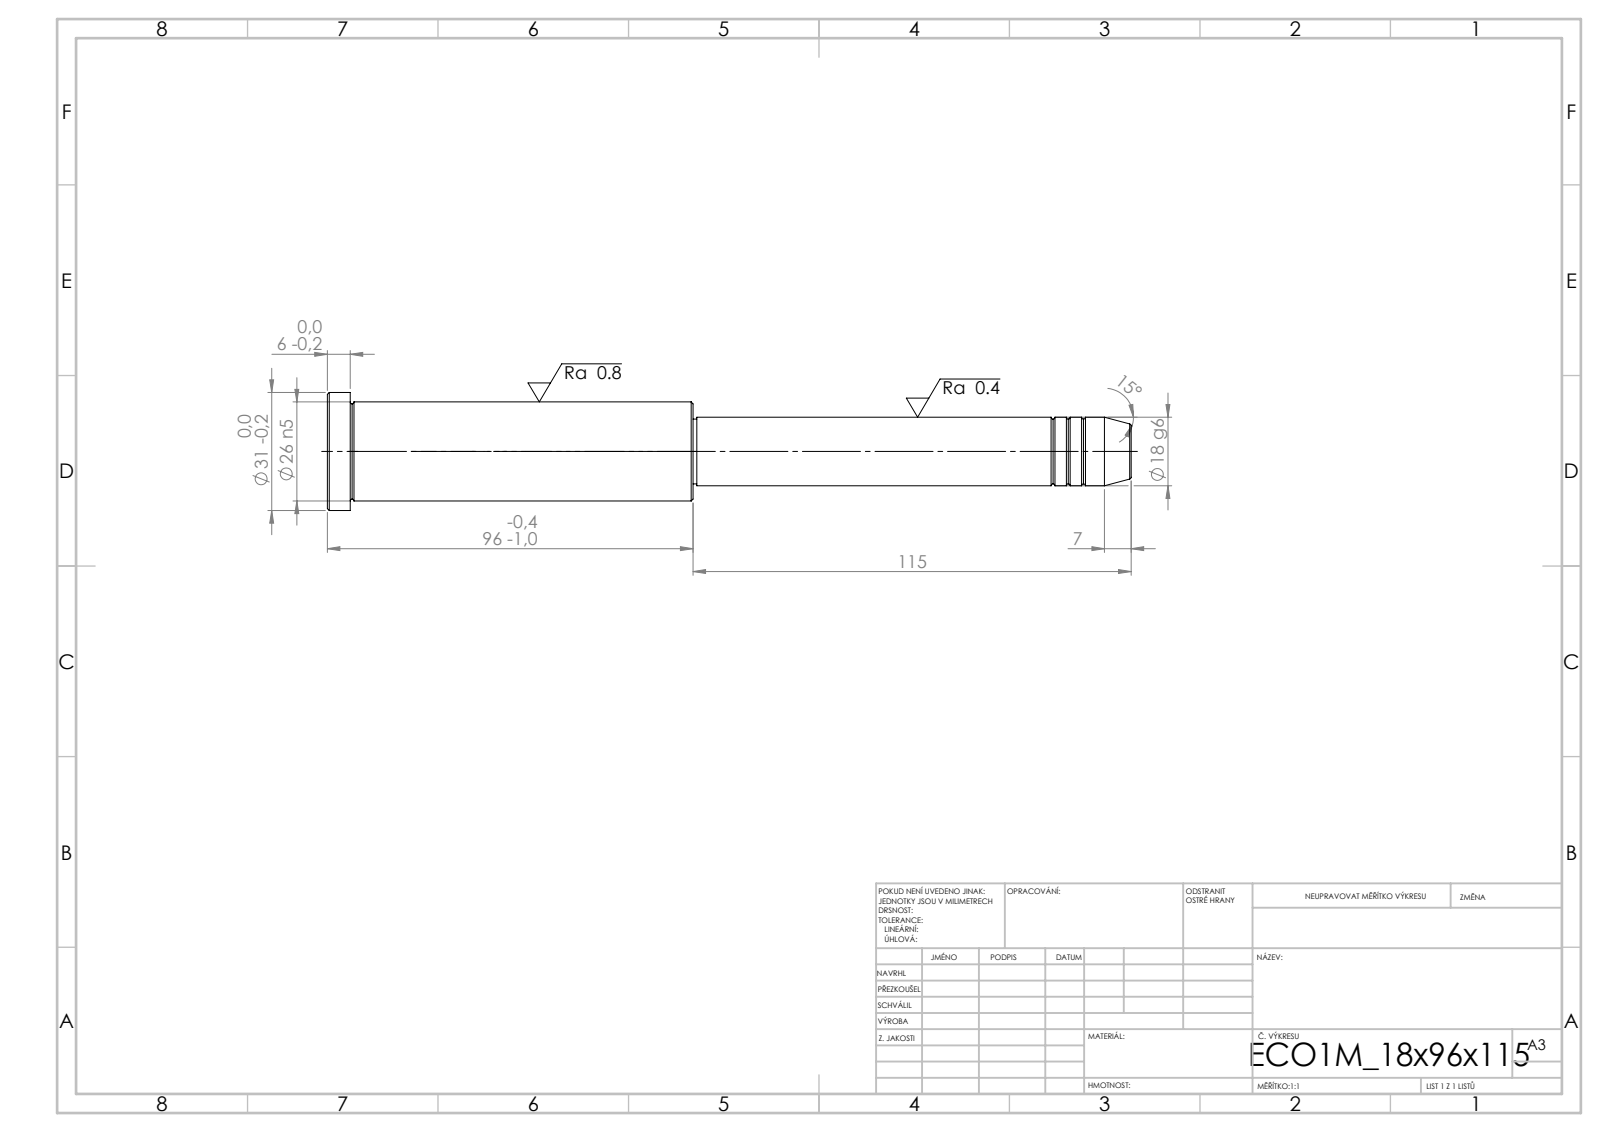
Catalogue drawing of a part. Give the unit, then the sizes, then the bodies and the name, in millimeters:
Units: millimetres
Overall size (bounding box): 211 × 31 × 31
Round bosses / shafts (diameter × count): ⌀31 ×1, ⌀26 ×1, ⌀18 ×1, ⌀17 ×1
Main face-to-face distances: 96, 90, 6, 115, 205, 211, 114, 1, 91, 97
Volume: 81 083 mm³ · Surface area: 15 949 mm²
Bodies: 1 solid, 43 faces (5 planar, 14 cylindrical, 24 other)
STEP written by: SolidWorks 2019 (CONFIG_CONTROL_DESIGN)
